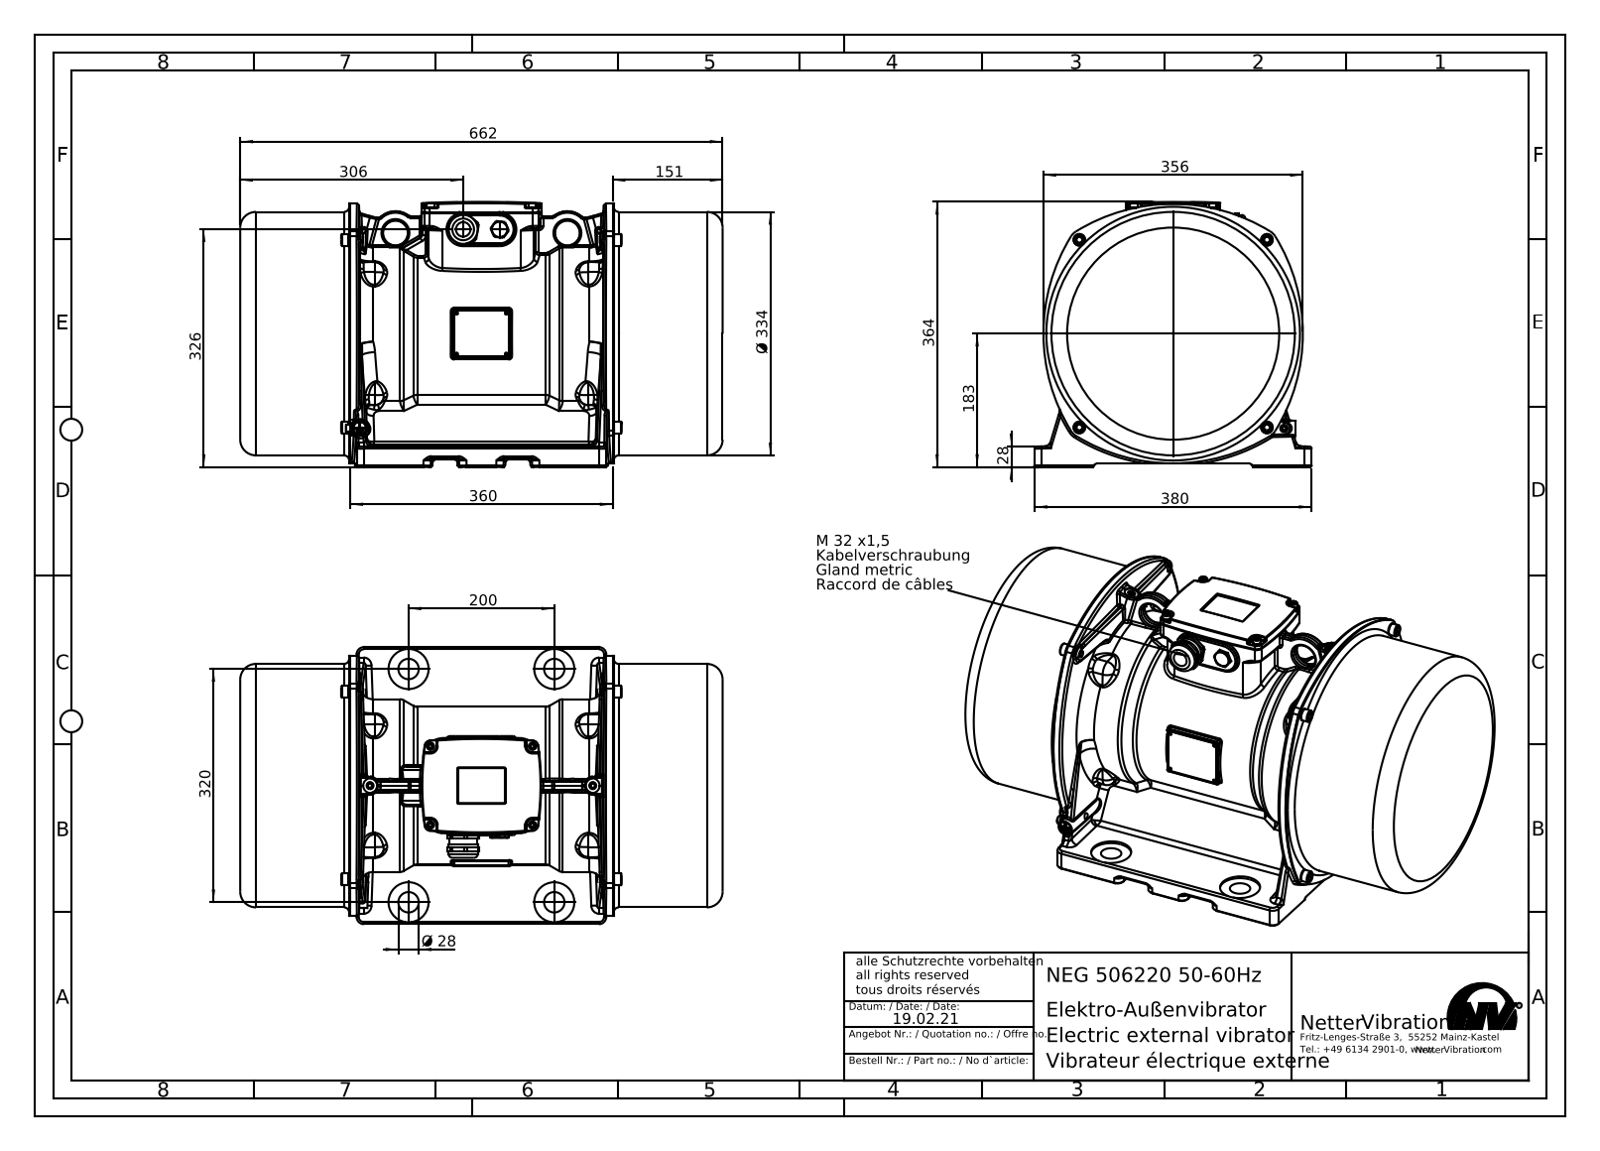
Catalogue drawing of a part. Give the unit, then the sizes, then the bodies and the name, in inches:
Units: inches
Overall size (bounding box): 26.063 × 14.961 × 14.323
Round holes (diameter × count): ⌀0.197 ×8, ⌀0.126 ×5, ⌀0.138 ×4, ⌀0.256 ×4, ⌀0.335 ×4, ⌀0.417 ×4, ⌀0.433 ×4, ⌀0.472 ×4, ⌀1.102 ×4, ⌀2.165 ×4, ⌀0.787 ×3, ⌀0.339 ×2
Round bosses / shafts (diameter × count): ⌀0.394 ×9, ⌀0.236 ×5, ⌀0.63 ×4, ⌀0.624 ×4, ⌀0.315 ×3, ⌀0.383 ×2, ⌀13.15 ×1, ⌀12.996 ×1
Partial cylindrical surfaces — rounded edges, fillets, slot ends (radius × count): R0.118 ×165, R0.039 ×33, R0.472 ×26, R0.059 ×24, R0.394 ×24, R0.079 ×23, R0.197 ×22, R0.787 ×16
Main face-to-face distances: 0.059, 26.004, 5.886, 20.118, 5.945, 20.059, 26.063, 25.945, 14.173, 0.512
Hole centre spacings: 8.55, 2.5, 4.337, 4.665, 6.598, 7.165, 7.887, 8.507
Volume: 538.1 in³ · Surface area: 3 641 in²
Bodies: 37 solids, 3618 faces (836 planar, 893 cylindrical, 1889 other)
Part name (STEP PRODUCT): NEG 506220-50-60 Hz
STEP written by: SolidWorks 2015 (AUTOMOTIVE_DESIGN)
